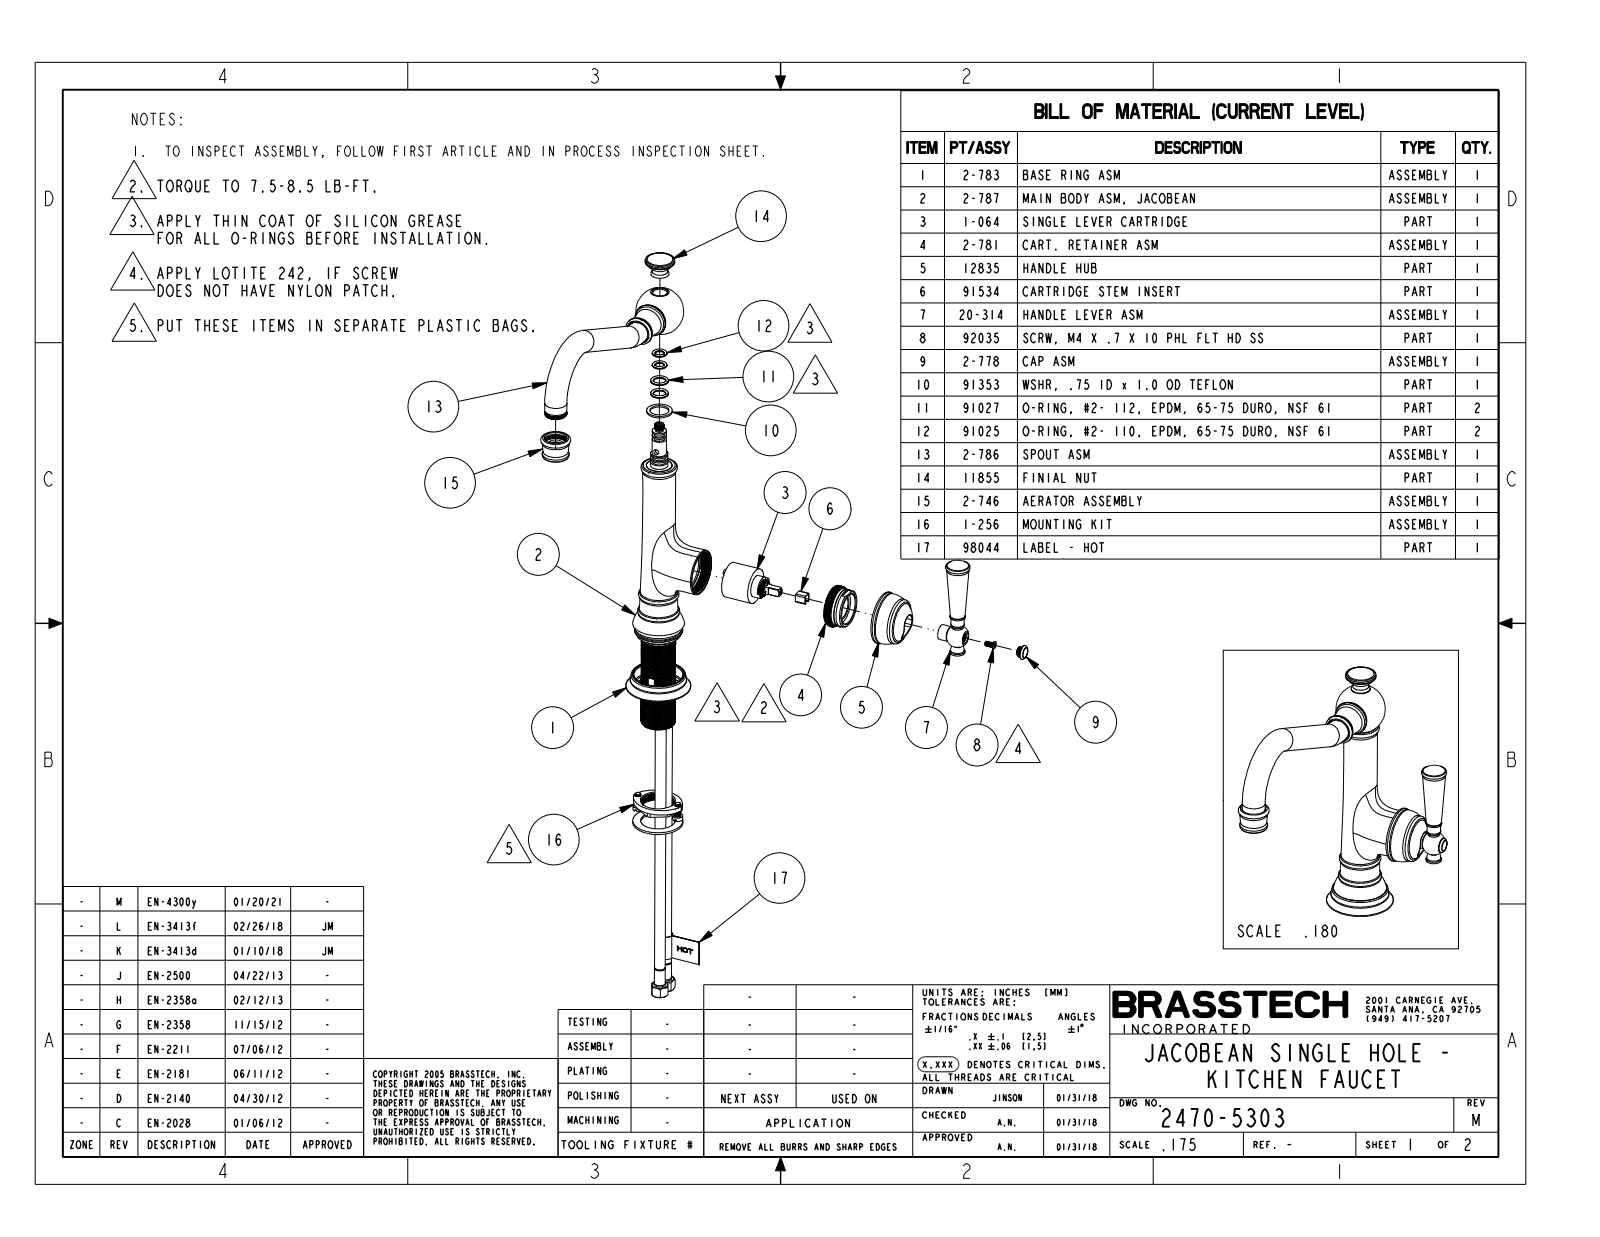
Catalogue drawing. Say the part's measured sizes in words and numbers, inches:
The part is named "2470-5313_ASM; 2470-5303_ASM". Its 3-D file was written by "CREO PARAMETRIC BY PTC INC, 2018400 (AUTOMOTIVE_DESIGN)". It is 4 solids with 534 faces: 55 planar, 144 cylindrical and 335 other. Overall it measures 10.919 by 10.88 by 4.909 inches. Its volume is 25.53 cubic inches and its surface area 161.7 square inches. Round holes: 3 of diameter 0.744, 2 of diameter 0.34, 2 of diameter 0.9, 1 of diameter 0.165, 1 of diameter 0.206, 1 of diameter 0.25, 1 of diameter 0.35, 1 of diameter 0.4, 1 of diameter 0.44, 1 of diameter 0.564, 1 of diameter 0.689, 1 of diameter 0.75. Round bosses or shafts: 3 of diameter 0.87, 1 of diameter 2.02, 1 of diameter 1.313, 1 of diameter 1.16, 1 of diameter 1.13, 1 of diameter 1, 1 of diameter 0.595, 1 of diameter 0.56. Partial cylindrical surfaces (rounded edges, fillets, slot ends): 4 of radius 0.062, 2 of radius 0.337, 1 of radius 0.125, 1 of radius 0.188, 1 of radius 0.191, 1 of radius 0.197, 1 of radius 0.45. The main face-to-face distances are 0.04, 0.45, 0.49, 0.5, 0.05, 0.54, 7.653, 7.674, 0.021, 8.374. The hole center spacings are 3.143, 9.054, 9.584.
